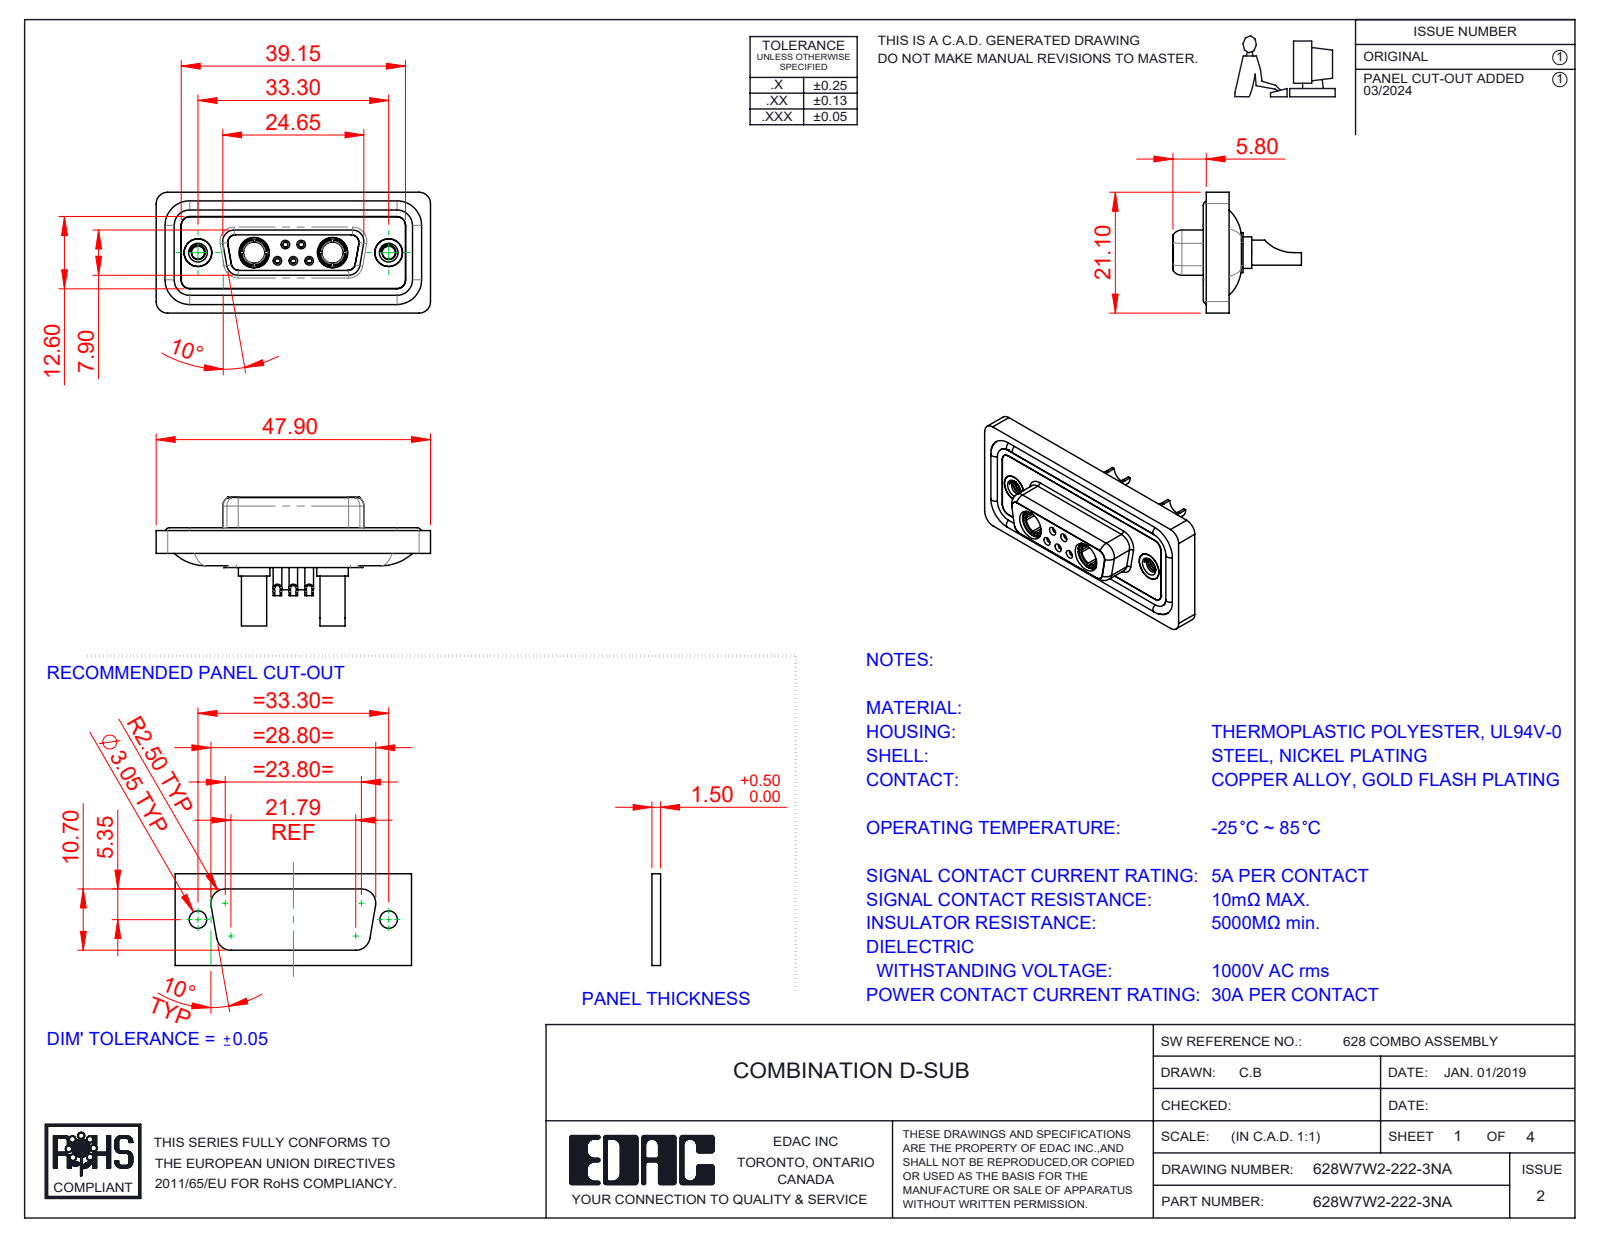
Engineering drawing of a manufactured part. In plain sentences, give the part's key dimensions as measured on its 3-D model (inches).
The part is named "Power Socket_30A SC; 628Combo Threaded Rivet_A; 628Combo Housing_7W2; 628Combo Contact Row 1_22 (+5 more)". Its 3-D file was written by "SolidWorks 2023 (CONFIG_CONTROL_DESIGN)". It is 16 solids with 819 faces: 254 planar, 347 cylindrical and 218 other. Overall it measures 1.886 by 0.884 by 0.831 inches. Its volume is 0.375 cubic inches and its surface area 15.74 square inches. Round holes: 5 of diameter 0.035, 5 of diameter 0.039, 5 of diameter 0.043, 5 of diameter 0.059, 5 of diameter 0.079, 4 of diameter 0.191, 3 of diameter 0.063, 2 of diameter 0.067, 2 of diameter 0.089, 2 of diameter 0.138, 2 of diameter 0.146, 2 of diameter 0.157. Round bosses or shafts: 6 of diameter 0.063, 5 of diameter 0.087, 2 of diameter 0.217, 2 of diameter 0.205, 2 of diameter 0.195, 2 of diameter 0.195, 2 of diameter 0.189, 2 of diameter 0.187. Partial cylindrical surfaces (rounded edges, fillets, slot ends): 22 of radius 0.059, 20 of radius 0.079, 12 of radius 0.053, 8 of radius 0.063, 6 of radius 0.039, 4 of radius 0.01, 4 of radius 0.02, 4 of radius 0.024. The main face-to-face distances are 0.016, 0.063, 0.071, 0.02, 0.114, 0.043, 0.293, 0.222, 0.26, 0.278. The hole center spacings are 0.124, 0.109, 0.386, 0.925, 0.17, 0.17, 0.198, 0.198.
